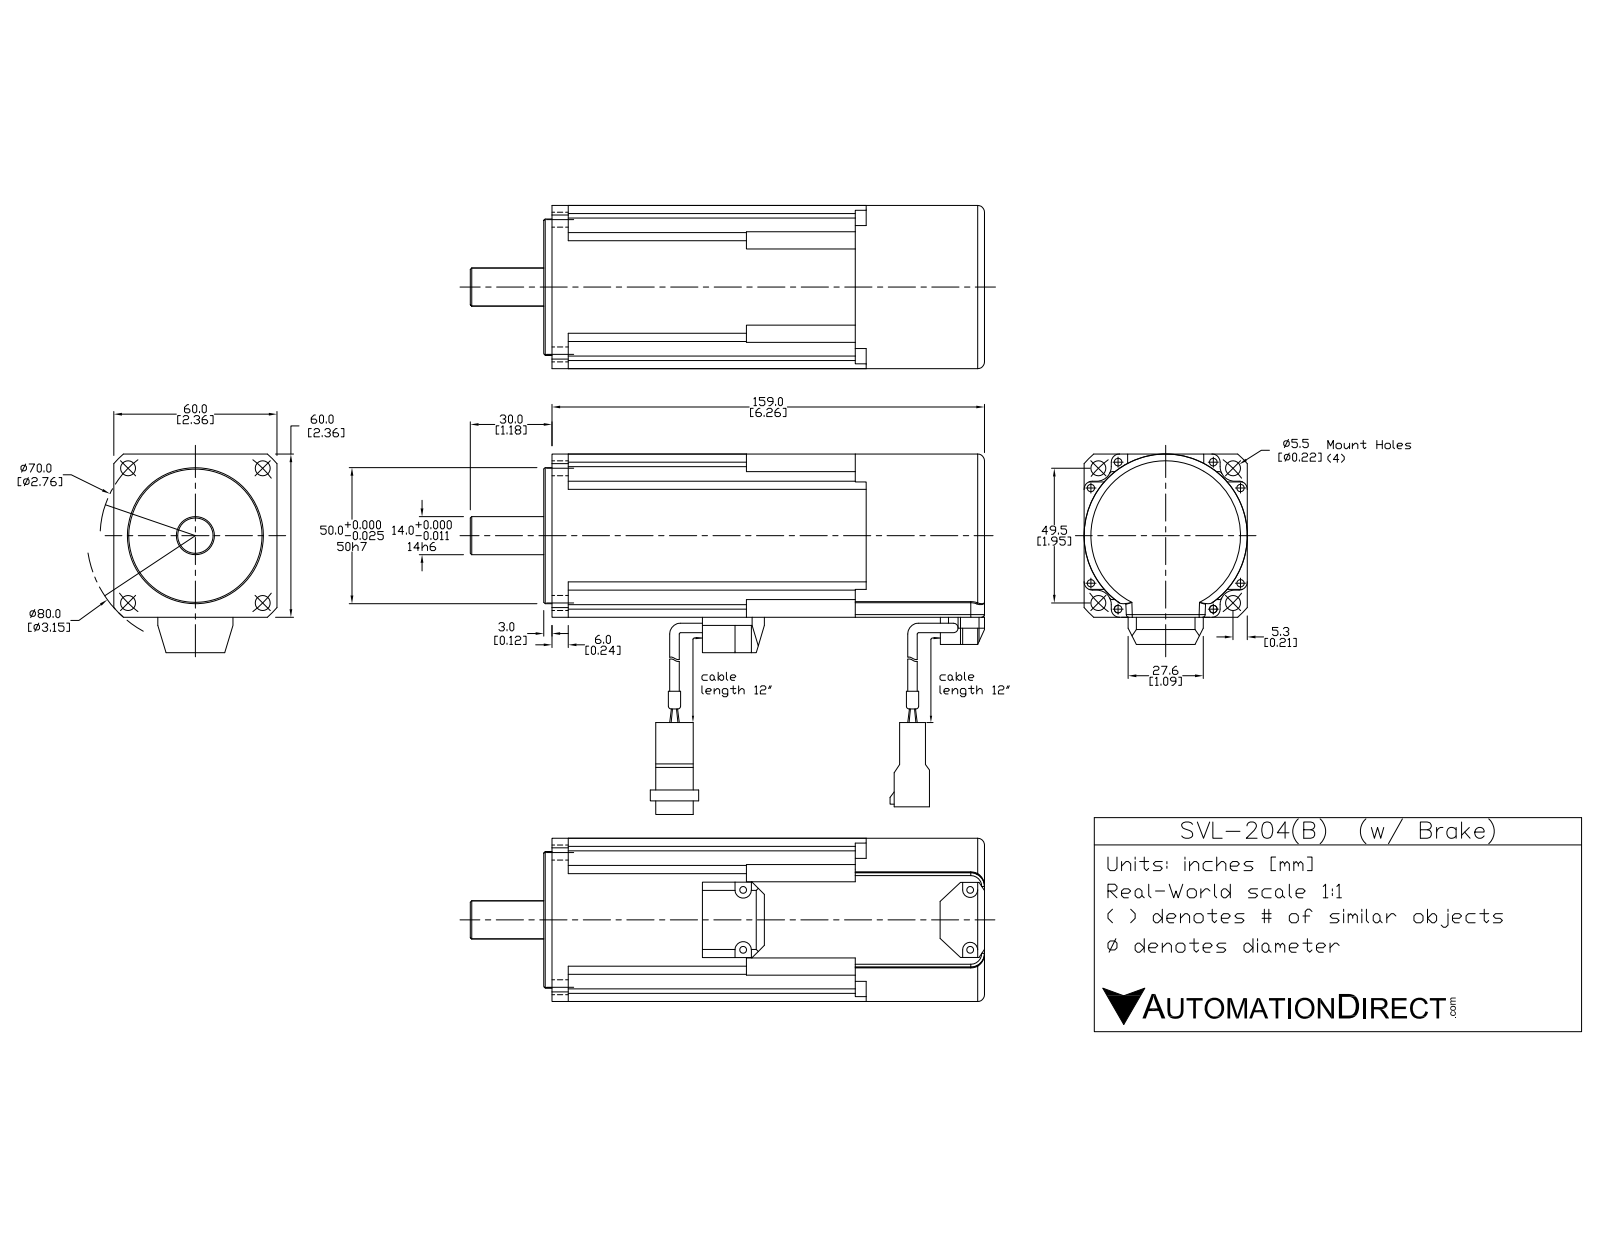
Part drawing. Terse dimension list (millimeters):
name: SVL-204B
written by: SolidWorks 2015 (AUTOMOTIVE_DESIGN)
unit: mm
bodies: 18 solids, 417 faces (245 planar, 137 cylindrical, 35 other)
size: 189 × 73.4 × 63.26
volume: 513 761 mm³; area: 68 387 mm²
holes: 4× ⌀5.5, 1× ⌀18.5
bosses: 5× ⌀5.5, 4× ⌀5, 4× ⌀3.5, 1× ⌀60, 1× ⌀50, 1× ⌀14, 1× ⌀7
rounds: 14× R1, 12× R3, 4× R2, 4× R2.5, 4× R2.75, 4× R5.3
face distances: 60, 55, 45.1, 100.1, 47.9, 93, 148, 69, 162, 114.1
hole spacings: 35, 49.5, 70
